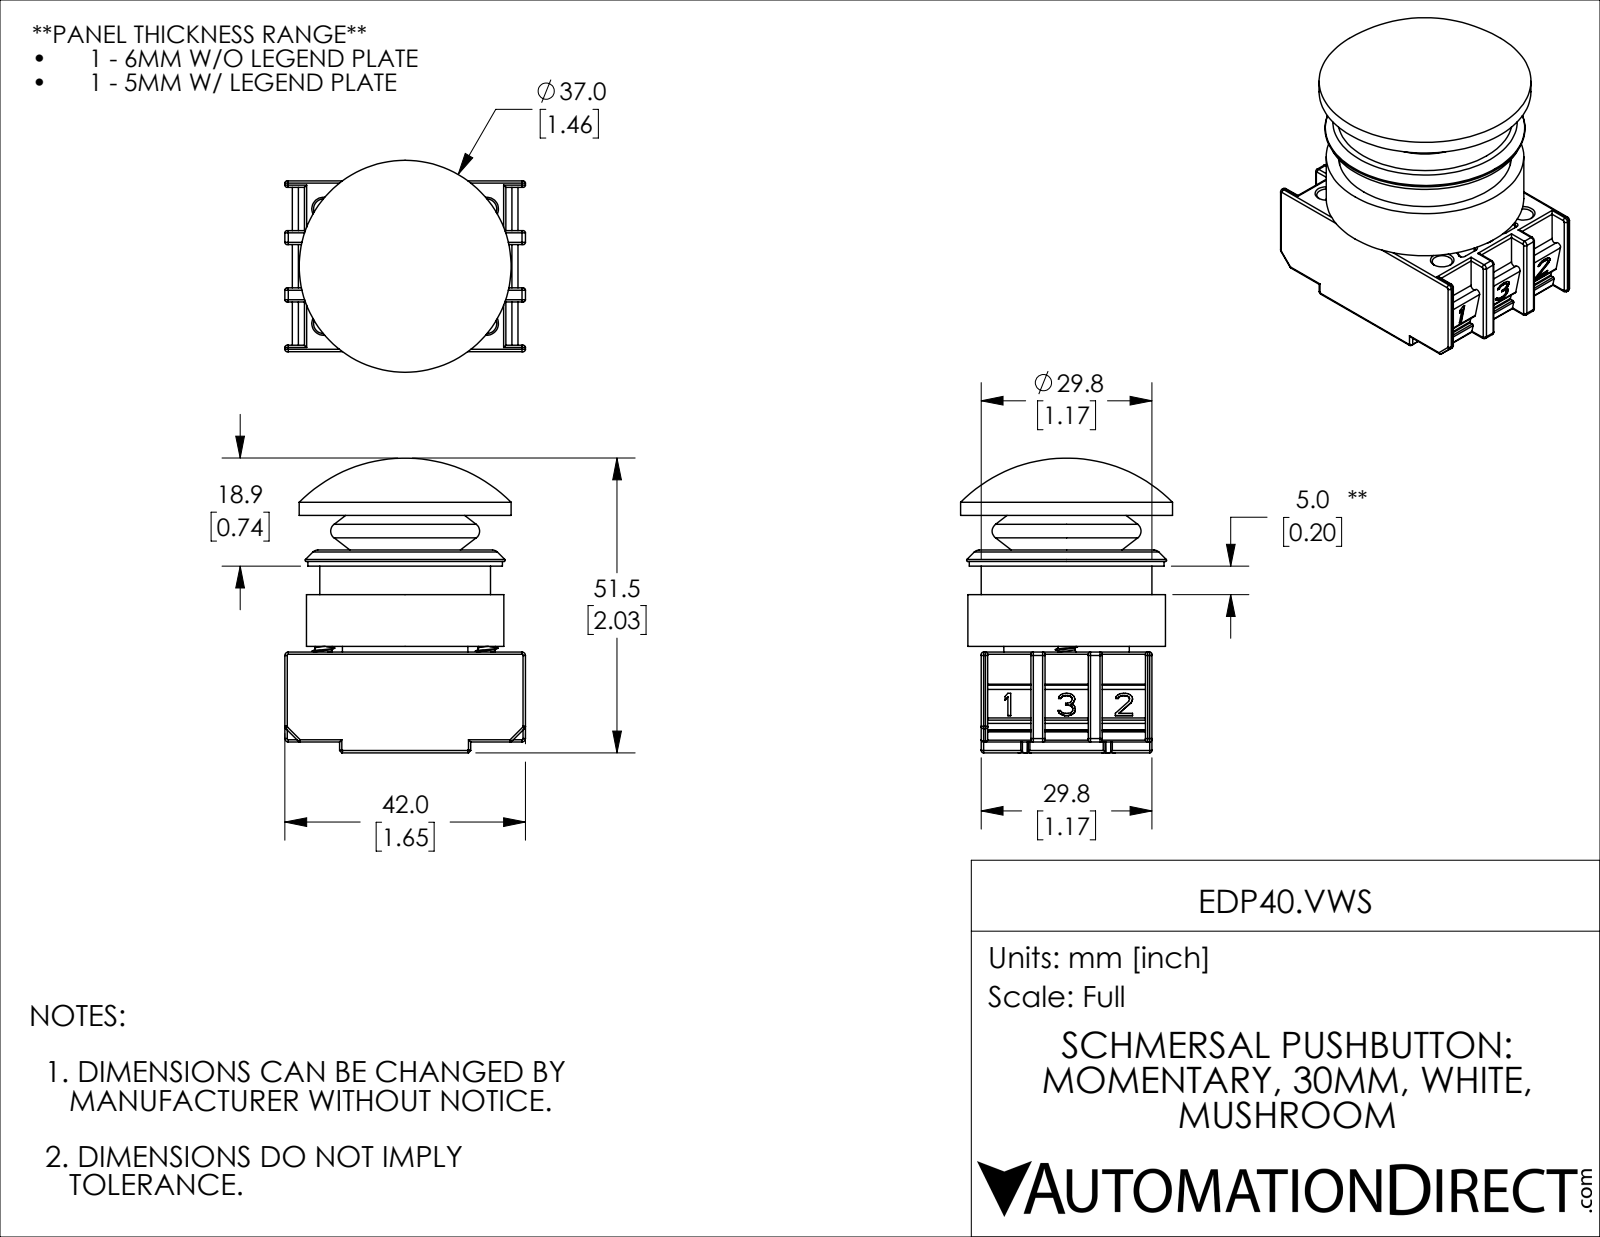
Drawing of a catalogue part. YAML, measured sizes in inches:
part_name: "EDP40.VWS"
step_written_by: "SolidWorks 2019 (CONFIG_CONTROL_DESIGN)"
units: inches
bodies: {solids: 5, faces: 1490, planar: 538, cylindrical: 503, other: 449}
overall_size: [2.026, 1.654, 1.457]
volume: 1.999
surface_area: 36.59
round_holes:
  - {diameter: 0.138, count: 6}
  - {diameter: 0.203, count: 6}
  - {diameter: 0.325, count: 1}
  - {diameter: 0.478, count: 1}
  - {diameter: 0.74, count: 1}
  - {diameter: 0.768, count: 1}
  - {diameter: 0.949, count: 1}
  - {diameter: 0.953, count: 1}
  - {diameter: 1.024, count: 1}
  - {diameter: 1.189, count: 1}
  - {diameter: 1.26, count: 1}
round_bosses_or_shafts:
  - {diameter: 0.189, count: 2}
  - {diameter: 0.115, count: 2}
  - {diameter: 1.457, count: 1}
  - {diameter: 1.358, count: 1}
  - {diameter: 1.339, count: 1}
  - {diameter: 1.173, count: 1}
  - {diameter: 1.004, count: 1}
  - {diameter: 0.945, count: 1}
partial_cylinders:
  - {radius: 0.016, count: 112}
  - {radius: 0.012, count: 48}
  - {radius: 0.008, count: 28}
  - {radius: 0.024, count: 8}
  - {radius: 0.02, count: 6}
  - {radius: 0.031, count: 6}
  - {radius: 0.004, count: 2}
  - {radius: 0.024, count: 2}
face_to_face_distances: [0.732, 1.173, 0.039, 0.075, 0.661, 0.693, 1.394, 0.701, 0.825, 0.394]
hole_center_spacings: [0.394, 0.685, 1.189, 1.122, 0.561, 0.787, 1.371]
